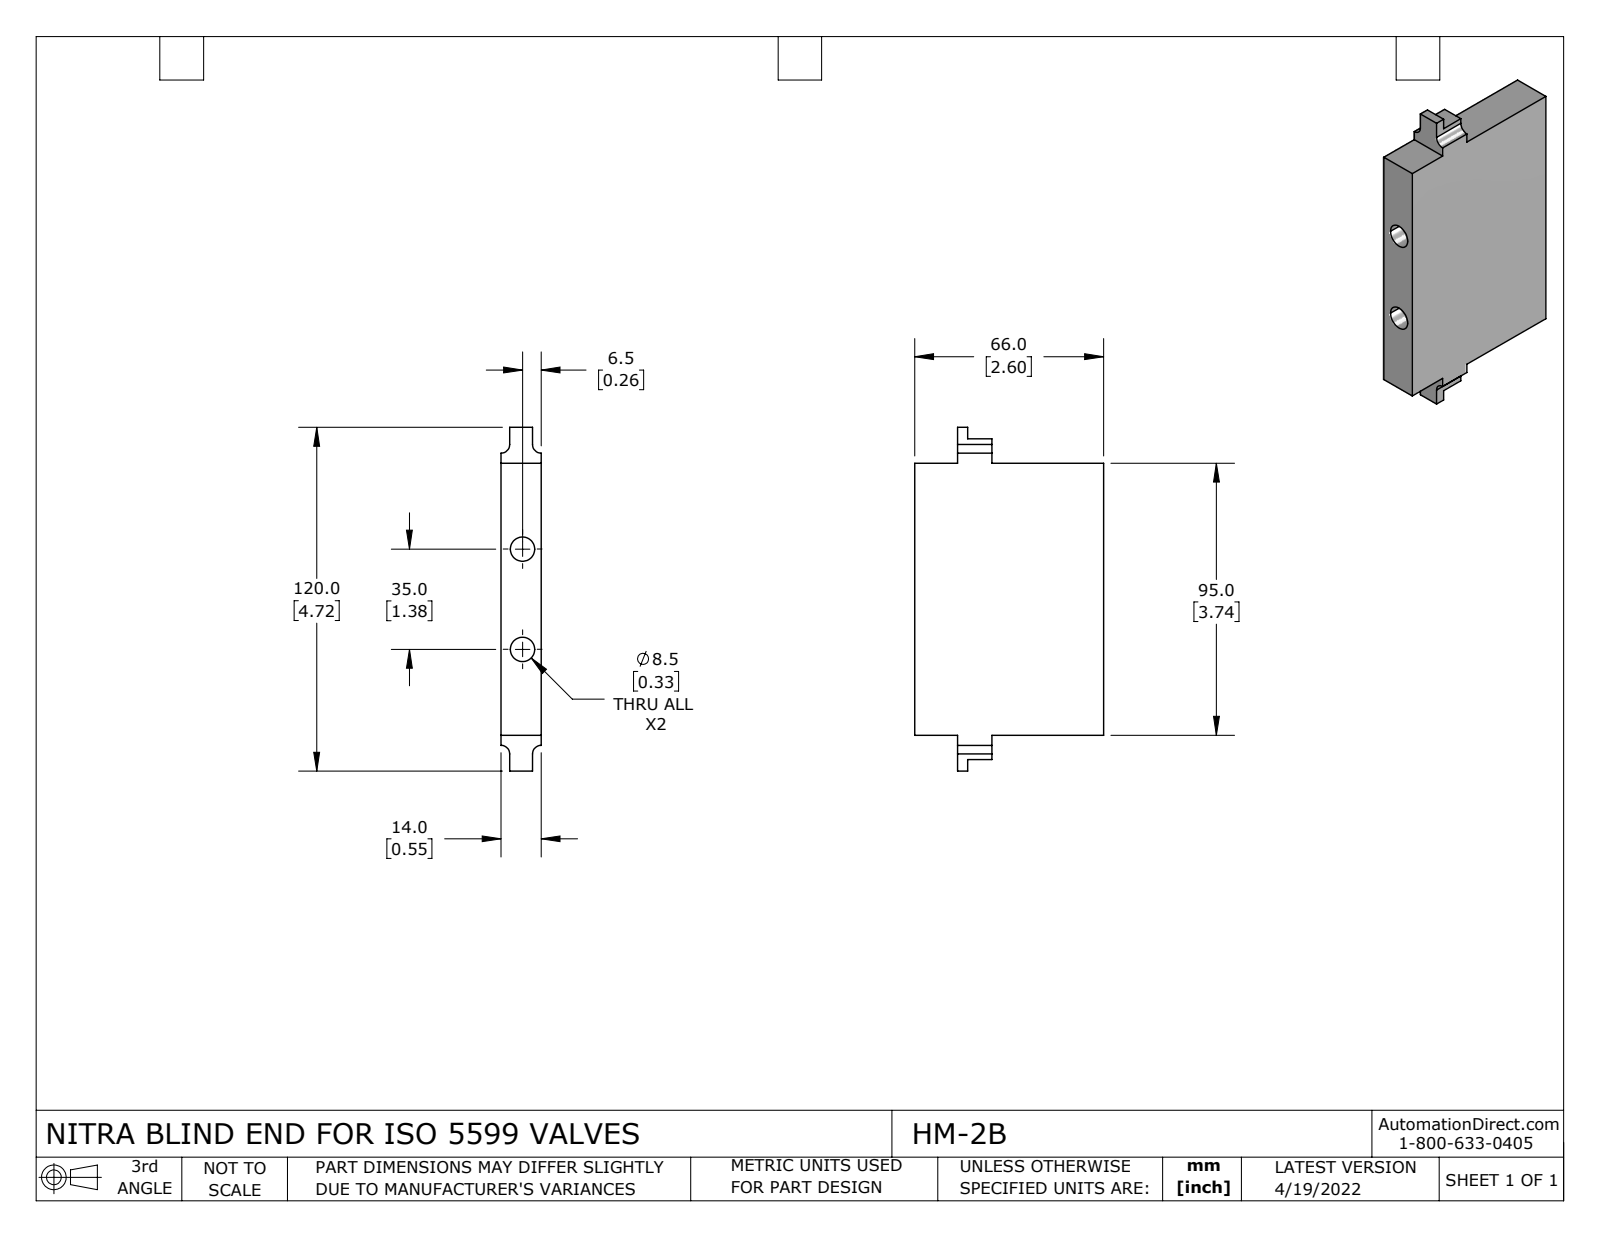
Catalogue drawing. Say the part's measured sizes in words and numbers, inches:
The part is named "HM-2B". Its 3-D file was written by "SolidWorks 2021 (CONFIG_CONTROL_DESIGN)". It is 1 solid with 39 faces: 25 planar, 14 cylindrical and 0 other. Overall it measures 4.724 by 2.598 by 0.551 inches. Its volume is 4.859 cubic inches and its surface area 33.85 square inches. Round holes: 3 of diameter 0.827, 2 of diameter 0.335. Partial cylindrical surfaces (rounded edges, fillets, slot ends): 4 of radius 0.118. The main face-to-face distances are 0.551, 2.598, 0.118, 0.433, 3.74, 2.008, 0.591, 0.335, 1.535, 0.472. The hole center spacings are 1.222, 1.378, 2.362.
